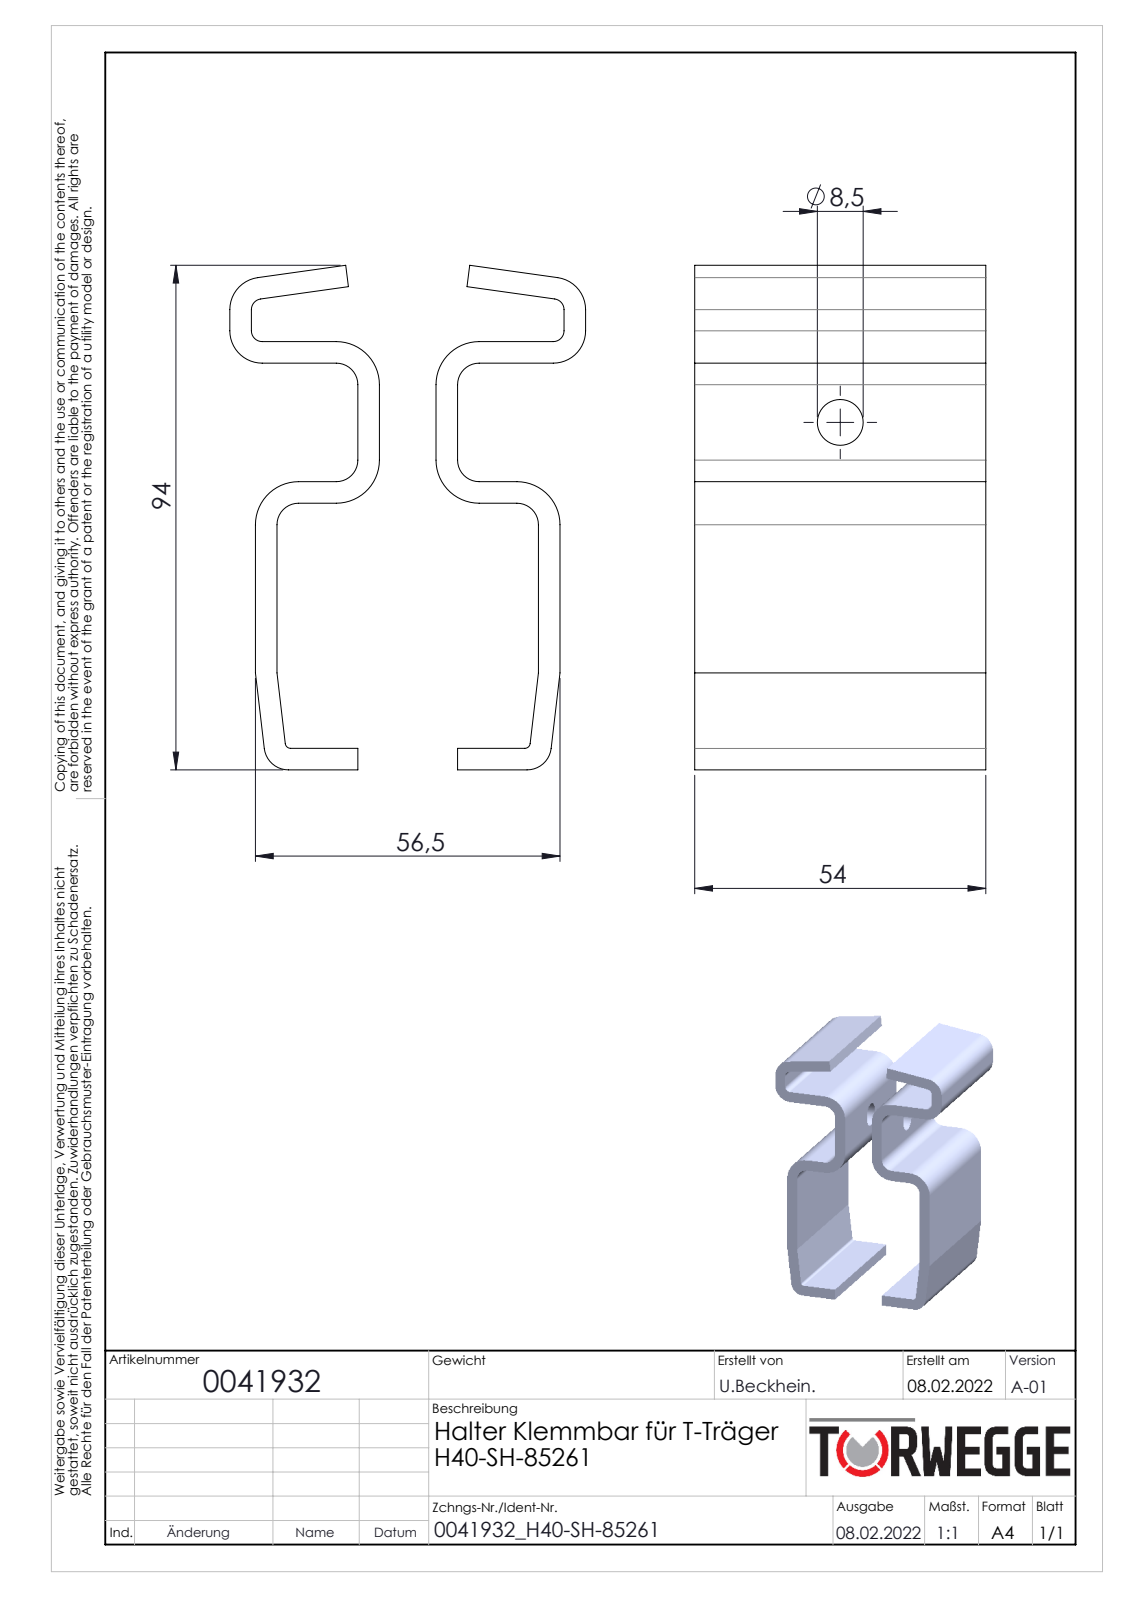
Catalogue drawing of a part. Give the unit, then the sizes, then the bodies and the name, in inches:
Units: inches
Overall size (bounding box): 3.688 × 2.598 × 2.126
Round holes (diameter × count): ⌀0.335 ×1
Partial cylindrical surfaces — rounded edges, fillets, slot ends (radius × count): R0.157 ×6, R0.315 ×6, R0.079 ×4, R0.236 ×4, R0.039 ×2, R0.177 ×2
Main face-to-face distances: 0.157, 0.748, 1.319, 2.067, 2.972, 1.476, 0.591, 1.949, 1.024, 1.909
Volume: 4.013 in³ · Surface area: 56.44 in²
Bodies: 2 solids, 68 faces (40 planar, 28 cylindrical, 0 other)
Part name (STEP PRODUCT): 0041932
STEP written by: SolidWorks 2020 (AUTOMOTIVE_DESIGN)
